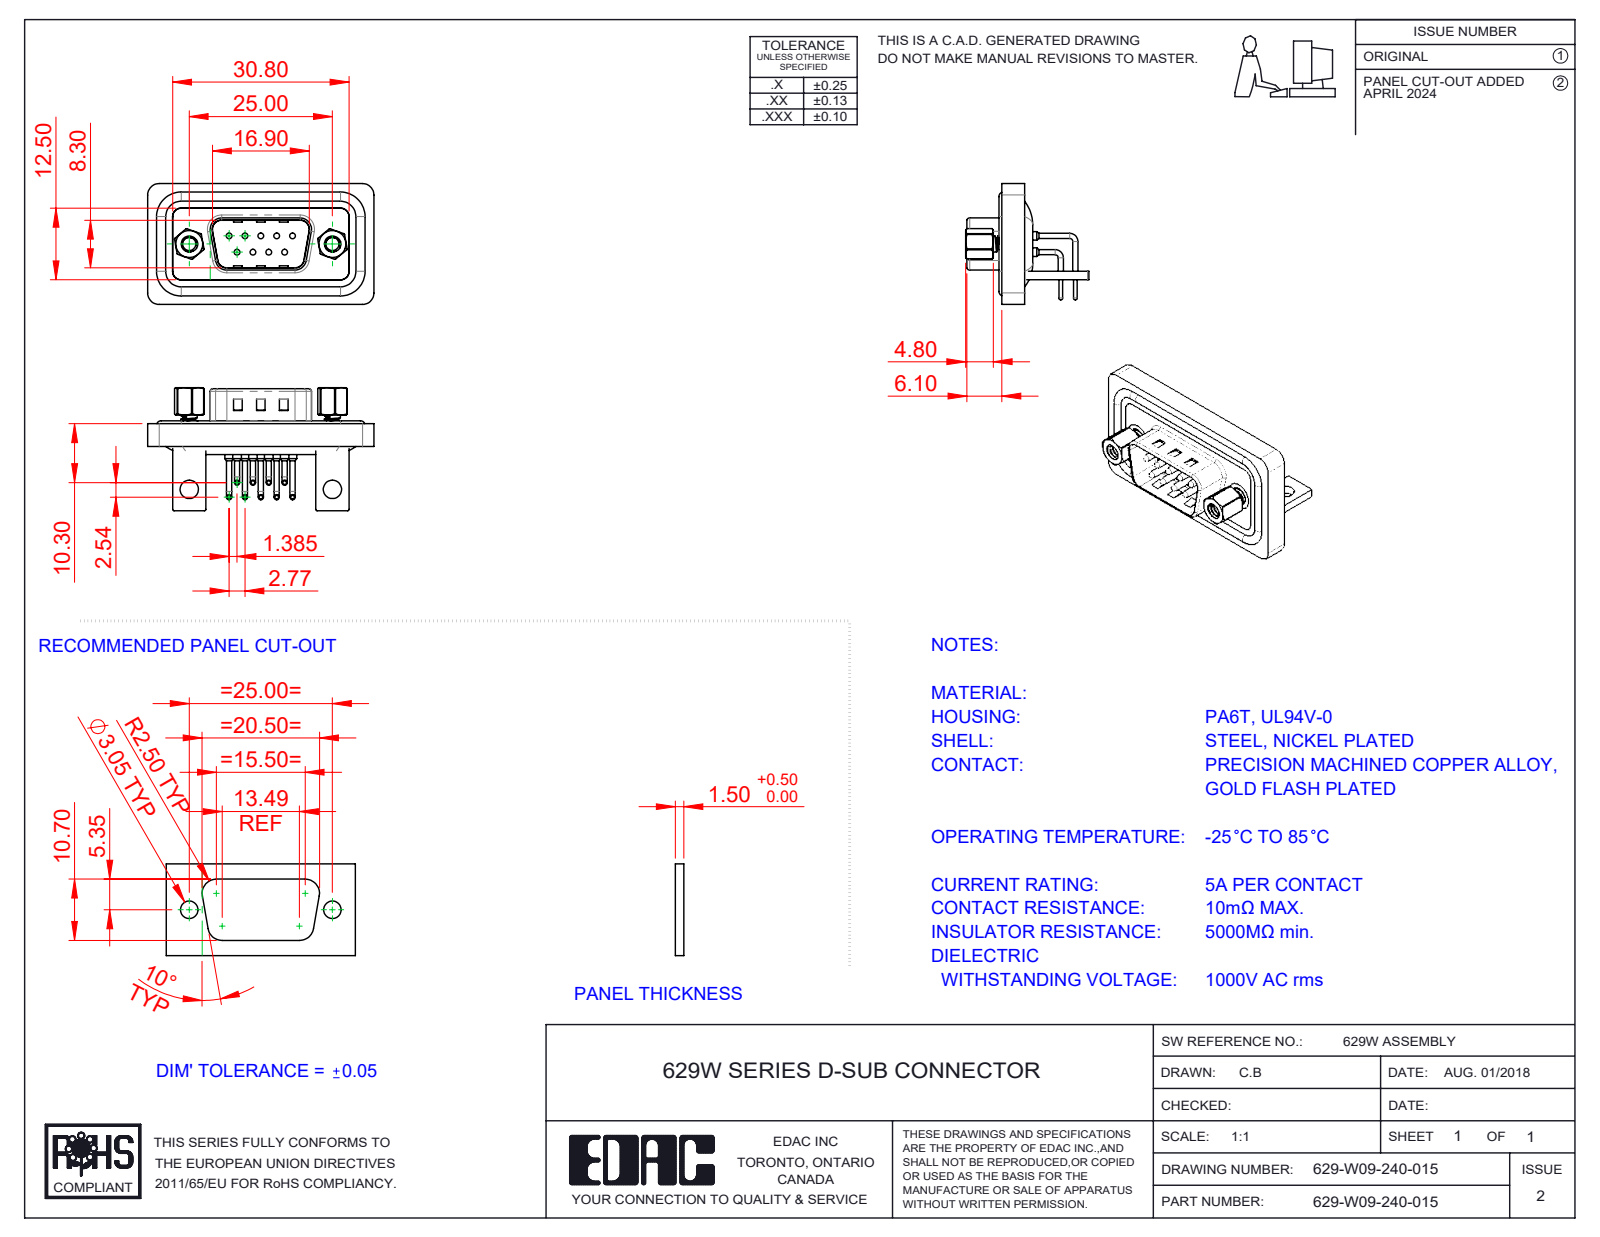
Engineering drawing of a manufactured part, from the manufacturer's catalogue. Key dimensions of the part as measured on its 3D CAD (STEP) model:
Part name (STEP PRODUCT): 629W Contact Row 1; 629W Stabilizer Bracket; 629W Waterproof Housing_09 Contacts; 629W Shell_09 Contacts (+5 more)
STEP written by: SolidWorks 2016 (CONFIG_CONTROL_DESIGN)
Units: millimetres
Bodies: 19 solids, 1502 faces (739 planar, 574 cylindrical, 189 other)
Overall size (bounding box): 39.51 × 21.3 × 21.1
Volume: 4 329 mm³ · Surface area: 7 331 mm²
Round holes (diameter × count): ⌀1 ×9, ⌀1.5 ×9, ⌀1.7 ×9, ⌀2 ×9, ⌀2.26 ×2, ⌀2.29 ×2, ⌀3.2 ×2, ⌀4 ×2, ⌀4.8 ×2, ⌀4.9 ×2, ⌀5 ×2
Round bosses / shafts (diameter × count): ⌀0.9 ×18, ⌀0.65 ×9, ⌀1.6 ×4, ⌀1.5 ×4, ⌀2.79 ×2, ⌀5 ×1
Partial cylindrical surfaces — rounded edges, fillets, slot ends (radius × count): R2 ×15, R1.5 ×14, R0.25 ×12, R0.5 ×9, R1.01 ×9, R2.7 ×6, R0.9 ×4, R1.6 ×4
Main face-to-face distances: 0.4, 1.6, 1.1, 2.9, 2.5, 4.3, 1.5, 5.8, 0.5, 4
Hole centre spacings: 3.16, 2.77, 5.54, 5.03, 5.04, 7.48, 7.49, 8.31
